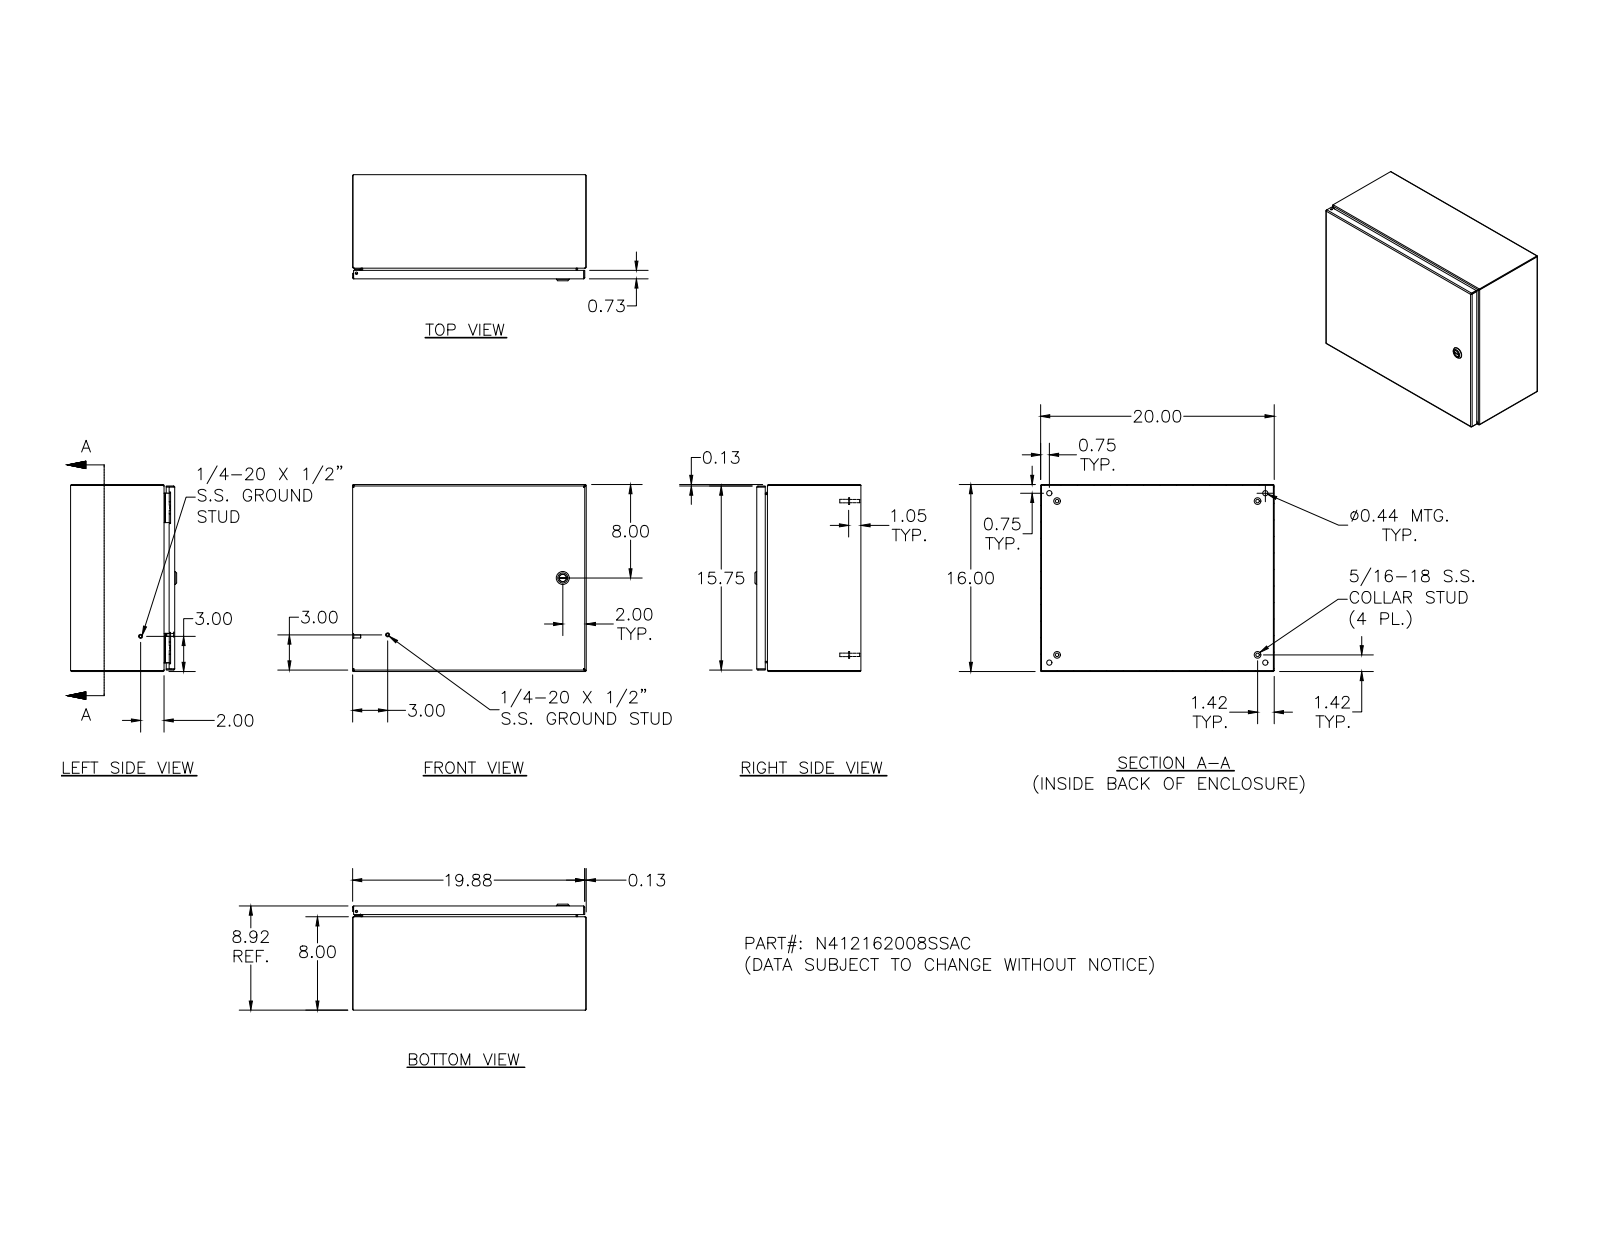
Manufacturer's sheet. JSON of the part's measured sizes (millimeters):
{"part_name": "N412162008SSAC; N412162008SSACBKP; 388151; N4121620SSACLID (+8 more)", "step_written_by": "Autodesk Inventor 2011 (AUTOMOTIVE_DESIGN)", "units": "millimeters", "bodies": {"solids": 34, "faces": 1364, "planar": 523, "cylindrical": 497, "other": 344}, "overall_size": [508, 406.4, 230.5], "volume_mm3": 1657000, "surface_area_mm2": 1775000, "round_holes": [[4.8, 5], [2.4, 4], [3.9, 4], [4.2, 4], [4.4, 4], [11.1, 4], [4, 2], [4.7, 1], [5, 1], [8, 1], [10, 1], [10.2, 1]], "round_bosses_or_shafts": [[6.4, 10], [14.3, 4], [9.1, 4], [8.1, 4], [7.6, 4], [7, 4], [6.5, 4], [4.2, 4]], "partial_cylinders_radius": [[1.3, 26], [0.4, 18], [0.4, 16], [2.3, 16], [0.8, 14], [3.2, 14], [0.5, 9], [0.8, 8]], "face_to_face_distances": [1.9, 224.6, 404.5, 222.7, 226.5, 506.1, 406.4, 402.6, 508, 504.2], "hole_center_spacings": [304.8, 0.4, 16.8, 479.3, 0.5, 12.7, 16.5, 16.6]}
